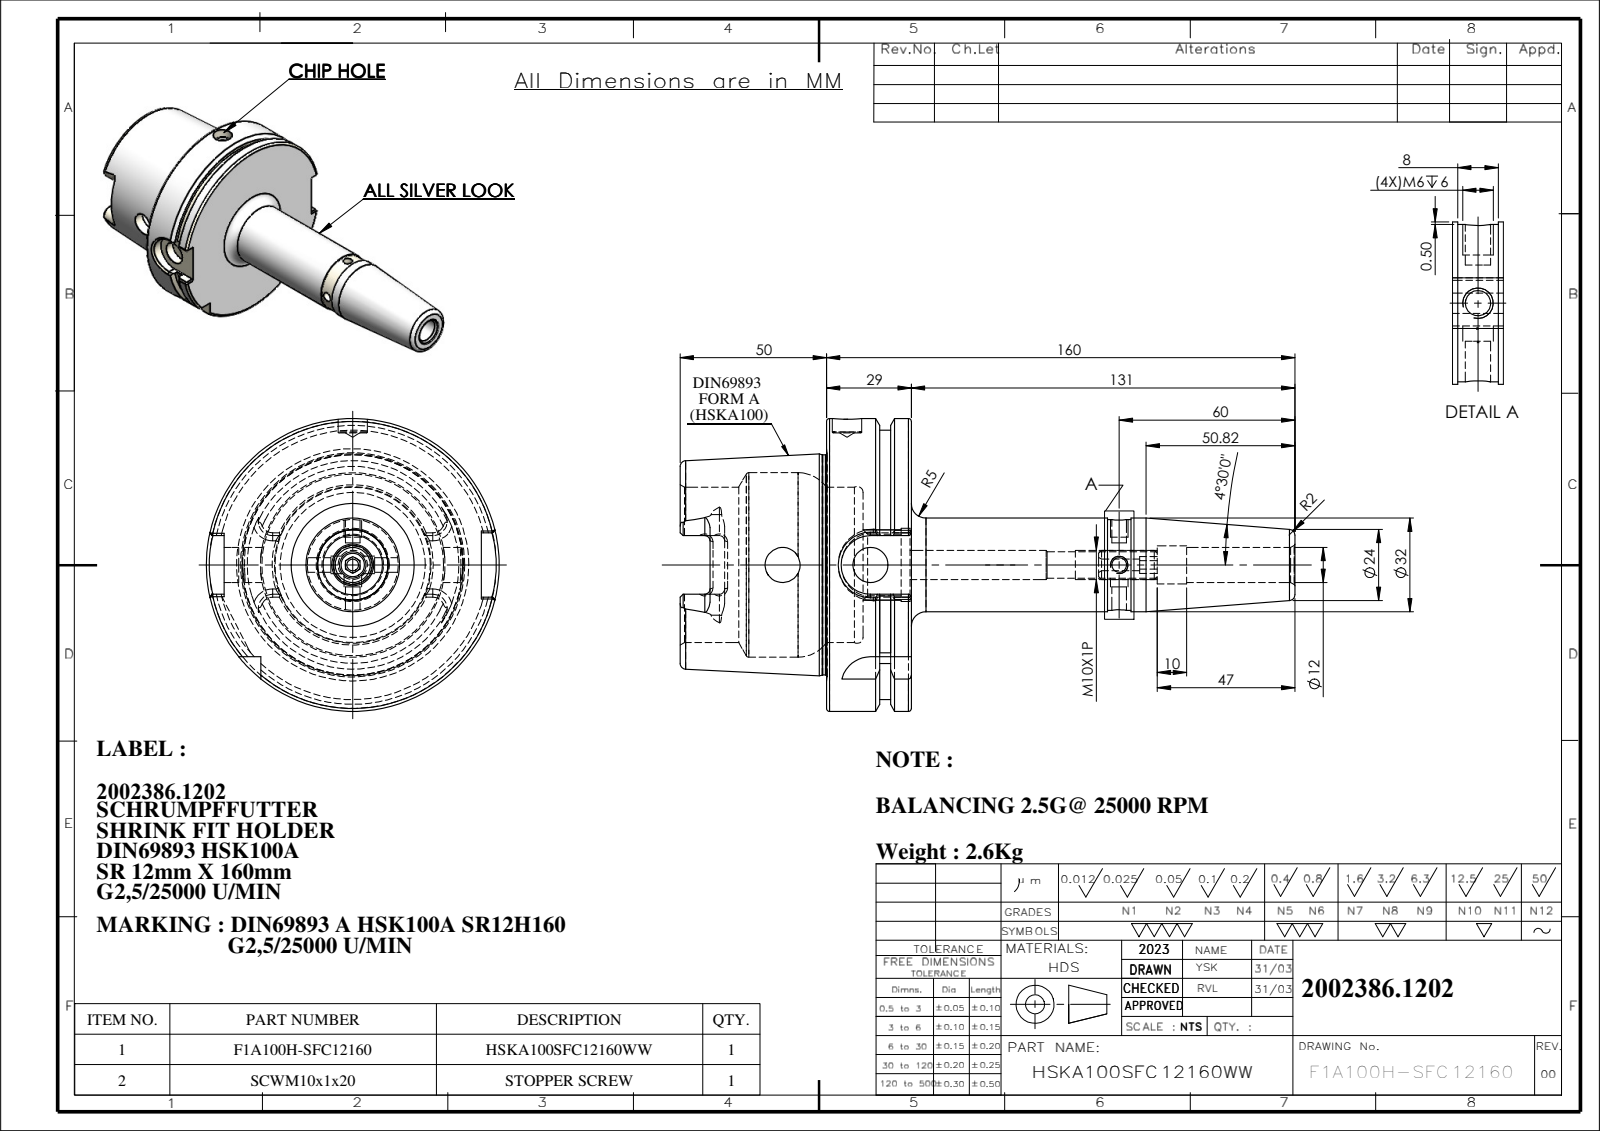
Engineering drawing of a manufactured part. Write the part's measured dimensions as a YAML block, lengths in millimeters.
part_name: "91100A-SR12160; HSKA100SFC12160WW; SCWM10X1"
step_written_by: "SolidWorks 2018 (CONFIG_CONTROL_DESIGN)"
units: millimeters
bodies: {solids: 2, faces: 218, planar: 68, cylindrical: 70, other: 80}
overall_size: [209.95, 100, 100]
volume: 338796
surface_area: 67610
round_holes:
  - {diameter: 5, count: 2}
  - {diameter: 10, count: 2}
  - {diameter: 12, count: 2}
  - {diameter: 4, count: 1}
  - {diameter: 9, count: 1}
  - {diameter: 11.98, count: 1}
  - {diameter: 12.98, count: 1}
  - {diameter: 21, count: 1}
  - {diameter: 25, count: 1}
  - {diameter: 53, count: 1}
  - {diameter: 63, count: 1}
round_bosses_or_shafts:
  - {diameter: 100, count: 1}
  - {diameter: 92, count: 1}
  - {diameter: 75.16, count: 1}
  - {diameter: 32, count: 1}
  - {diameter: 31, count: 1}
partial_cylinders:
  - {radius: 1.8, count: 6}
  - {radius: 4.88, count: 4}
  - {radius: 10, count: 2}
  - {radius: 11, count: 1}
face_to_face_distances: [28.95, 12.5, 16.45, 50, 62.5, 78.95, 16, 78.5, 28.5, 0.45]
hole_center_spacings: [30, 84.95, 92.95, 114.95]
